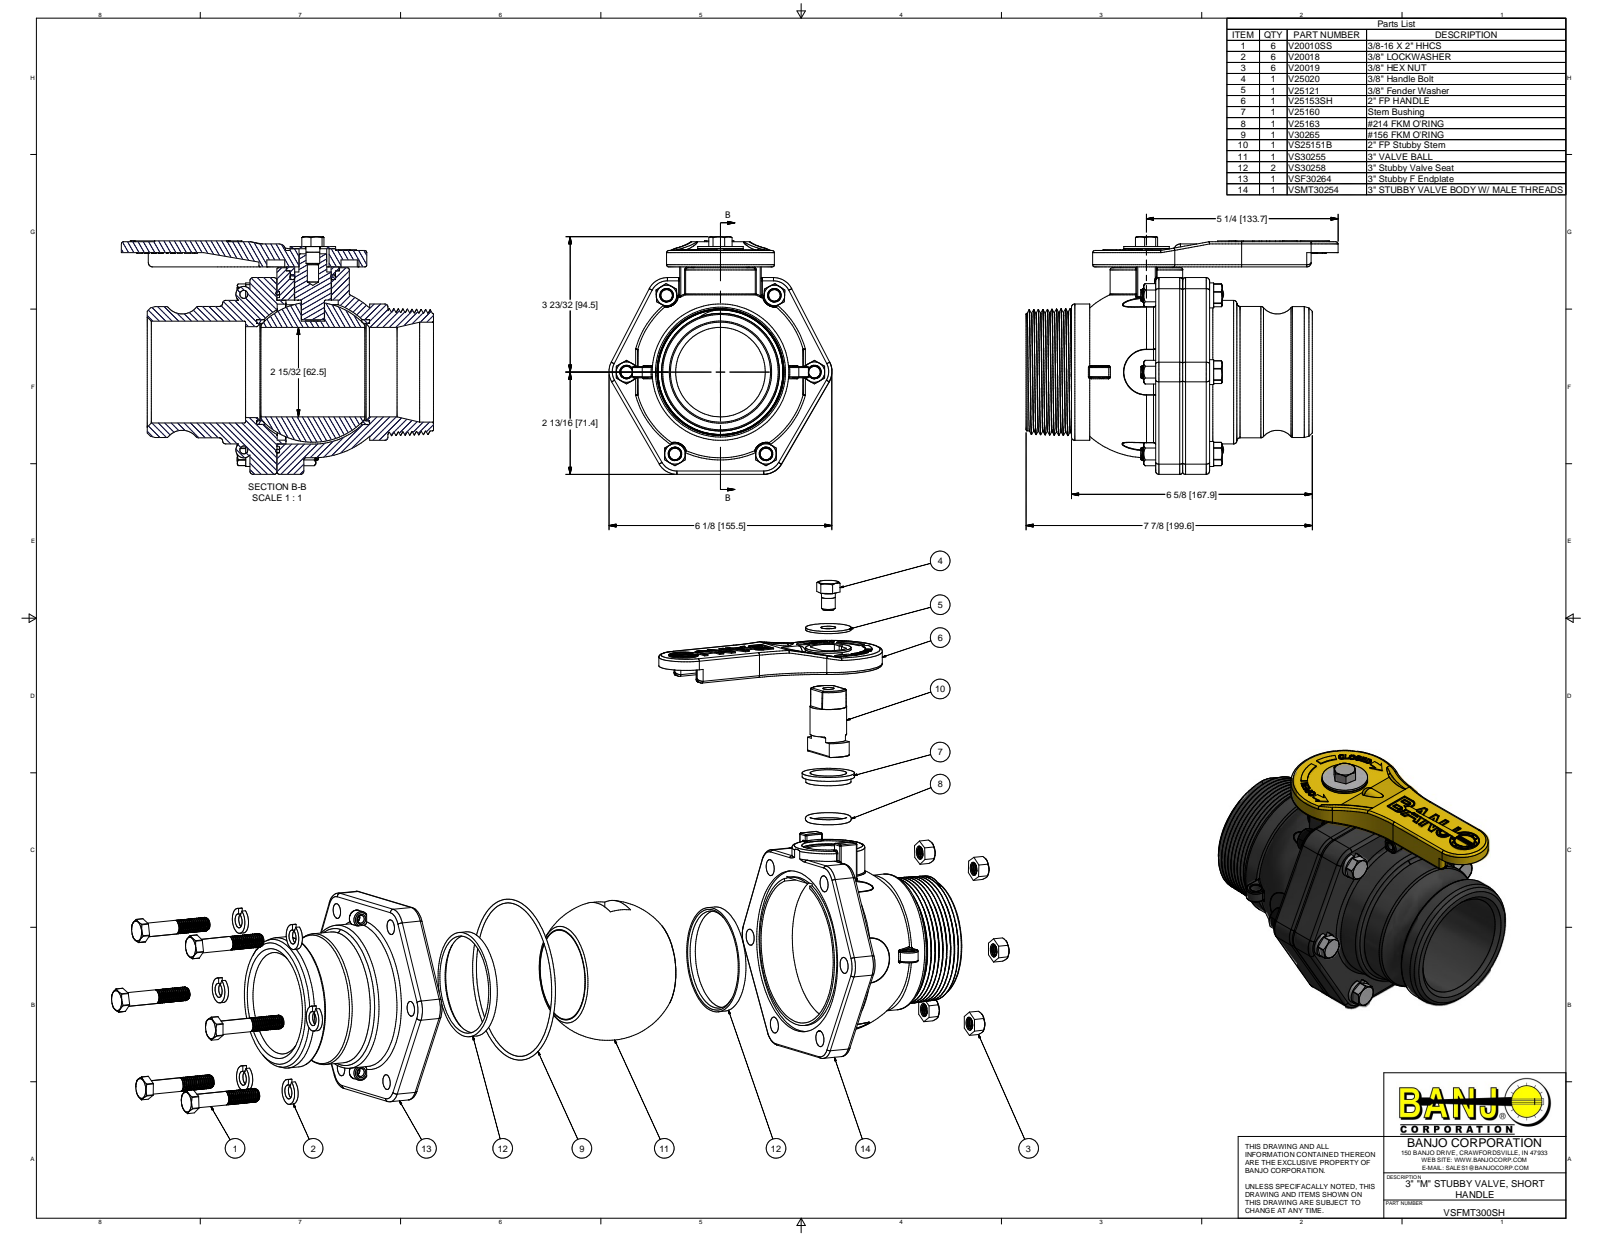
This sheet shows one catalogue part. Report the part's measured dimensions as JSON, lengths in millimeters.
{"part_name": "VSMT30254X; VSMT30254; VSF30264X; VSF30264 (+8 more)", "step_written_by": "Autodesk Inventor 2016 (AP203_CONFIGURATION_CONTROLLED_3D_DESIGN_OF_MECHANICAL_PARTS_AND_ASSEMBLIES_MIM_LF)", "units": "millimeters", "bodies": {"solids": 30, "faces": 2903, "planar": 1158, "cylindrical": 810, "other": 935}, "overall_size": [217.68, 165.91, 155.54], "volume_mm3": 1222000, "surface_area_mm2": 291349, "round_holes": [[10.31, 7], [7.81, 6], [9.78, 6], [11.18, 6], [5.54, 2], [7.87, 2], [7.8, 1], [13.83, 1], [19.55, 1], [25.4, 1], [25.81, 1], [31.5, 1]], "round_bosses_or_shafts": [[8.24, 90], [9.52, 7], [17.46, 6], [104.09, 1], [100.33, 1], [100.2, 1], [95.25, 1], [91.76, 1]], "partial_cylinders_radius": [[0.76, 39], [2.29, 24], [4.12, 12], [14.29, 10], [1.52, 8], [0.81, 6], [8.12, 6], [3.05, 5]], "face_to_face_distances": [18.79, 37.59, 18.8, 12.7, 6.09, 17.52, 4.82, 6.61, 11.43, 90.42], "hole_center_spacings": [60.44, 63.82, 65.38, 65.46, 65.53, 66.39, 110.89, 112.83]}
